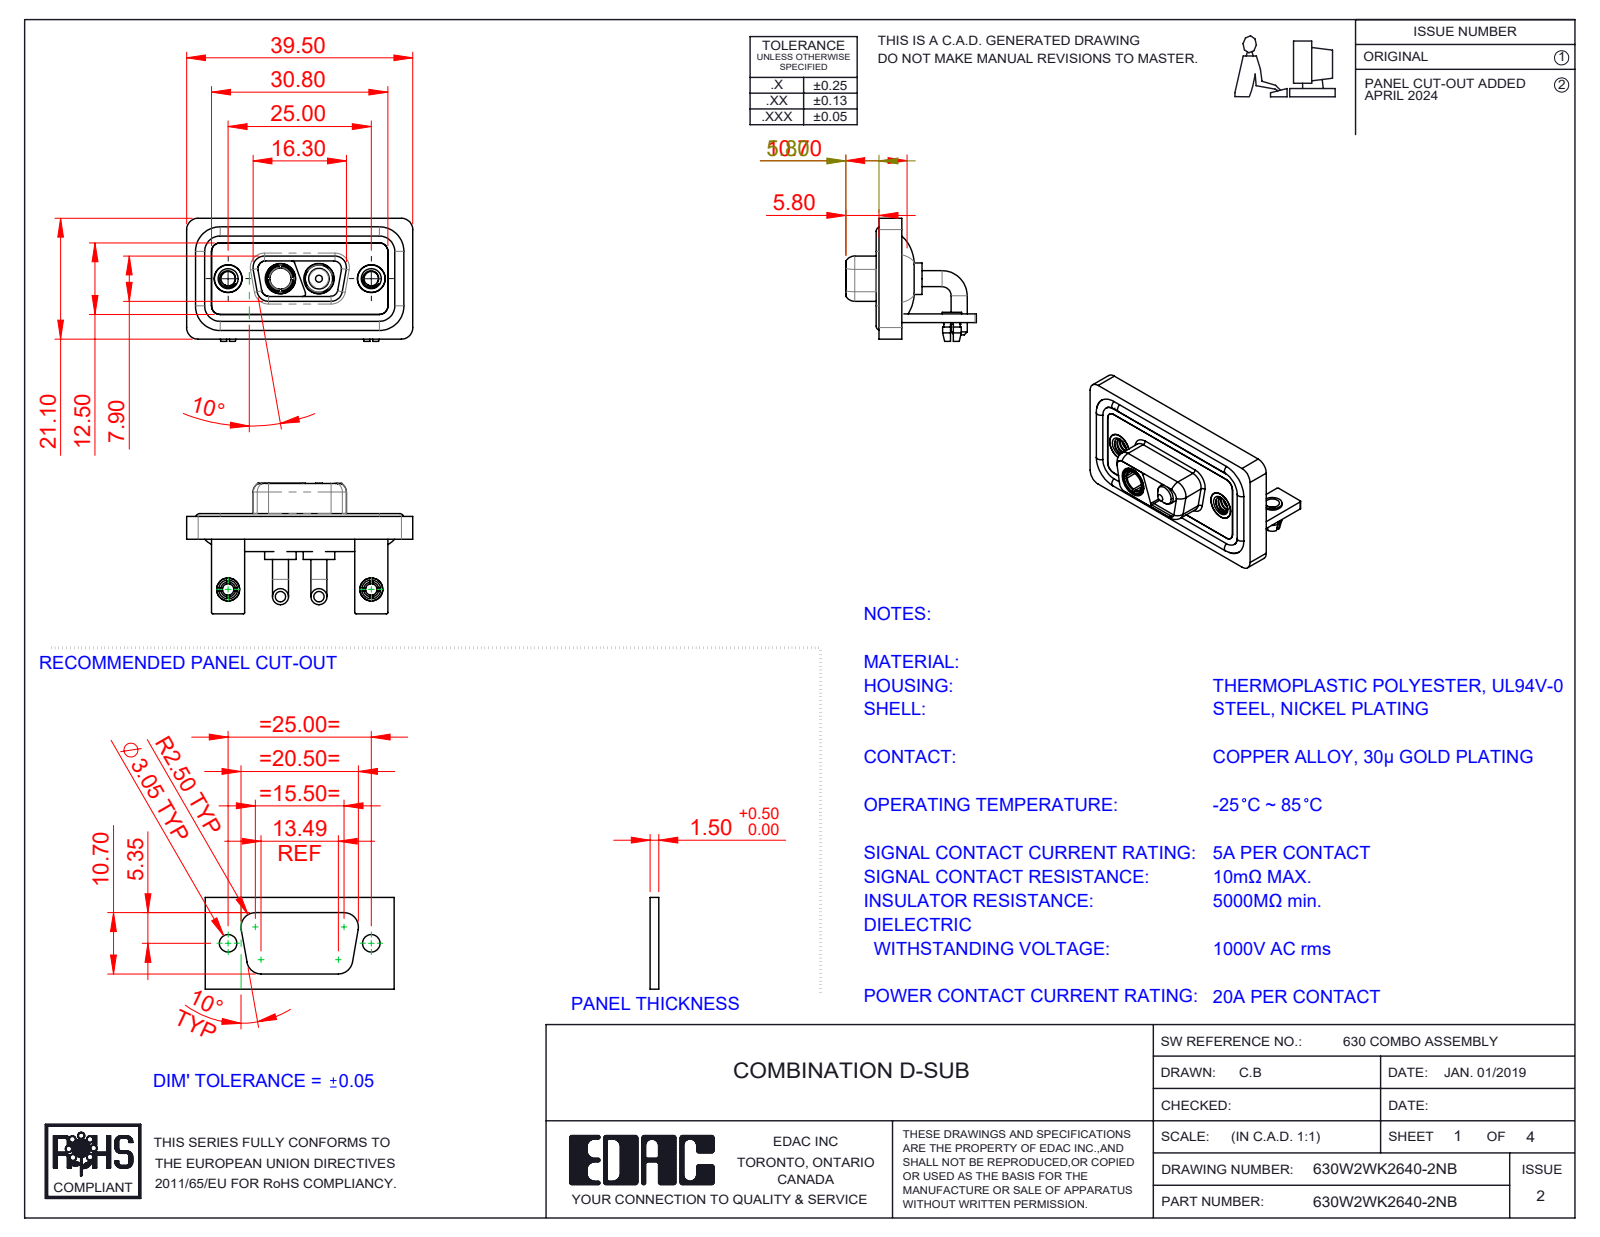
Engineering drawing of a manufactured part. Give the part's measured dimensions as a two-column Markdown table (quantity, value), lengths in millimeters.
| quantity | value |
| --- | --- |
| part name | 630Combo Board Lock_50 Contacts; Power Pin_20A RA; 630Combo Threaded Rivet_A; 630W2WK2640-2NB (+6 more) |
| STEP written by | SolidWorks 2023 (CONFIG_CONTROL_DESIGN) |
| units | millimeters |
| bodies | 15 solids, 642 faces (212 planar, 289 cylindrical, 141 other) |
| overall size | 39.5 × 22.8 × 21.5 |
| volume | 5 102 mm³ |
| surface area | 8 443 mm² |
| round holes (diameter × count) | 2.5 × 4, 4.85 × 4, 2 × 2, 3.2 × 2, 4 × 2, 4.05 × 2, 5 × 2, 5.3 × 2, 3.7 × 1 |
| round bosses / shafts (diameter × count) | 2.8 × 4, 1.6 × 4, 5.5 × 2, 5.2 × 2, 4.95 × 2, 4.8 × 2, 4.75 × 2, 4 × 2 |
| partial cylindrical surfaces (radius × count) | 2 × 19, 1.5 × 18, 0.25 × 16, 1.35 × 8, 1.6 × 8, 0.5 × 7, 0.6 × 4, 0.65 × 4 |
| main face-to-face distances | 0.4, 2.9, 1.5, 1.1, 3.7, 1.8, 0.8, 2.5, 1.6, 3.1 |
| hole center spacings | 9.14, 15.86, 25, 6.72 |
